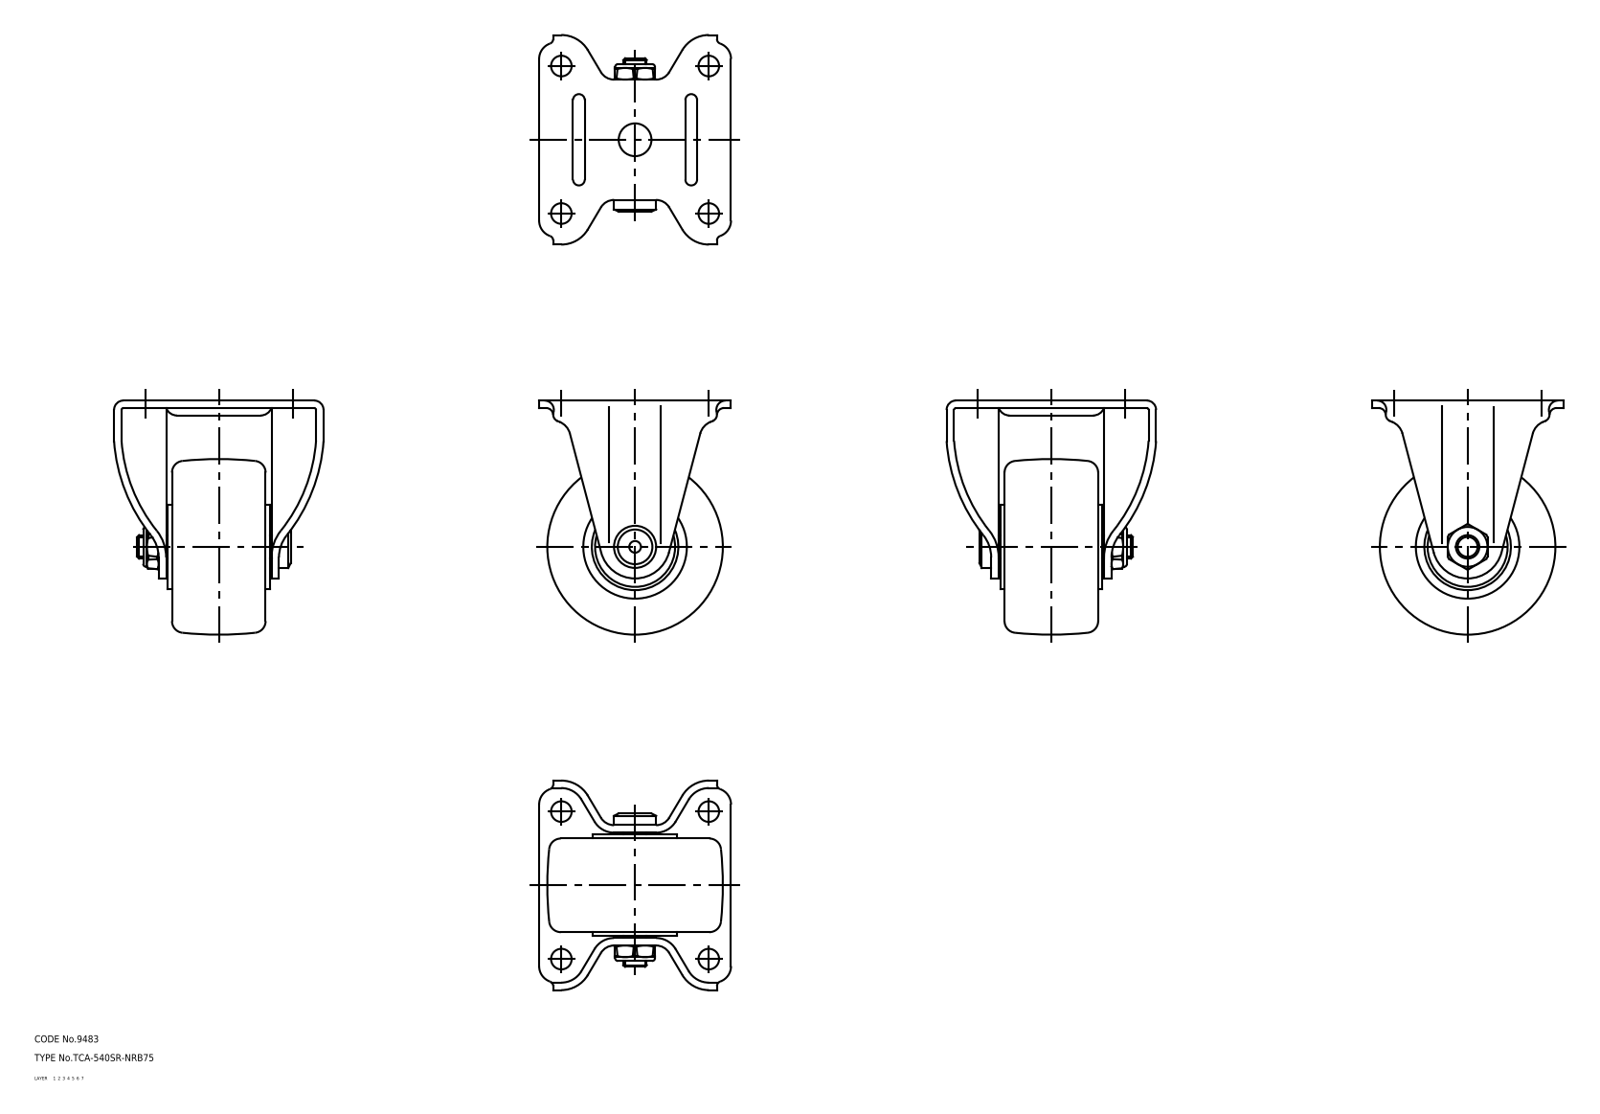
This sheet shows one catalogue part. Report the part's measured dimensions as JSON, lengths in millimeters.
{"part_name": "wheel; axle; No_540SR_NRB75_1298_36", "step_written_by": "CADfix (AUTOMOTIVE_DESIGN)", "units": "millimeters", "bodies": {"solids": 3, "faces": 245, "planar": 0, "cylindrical": 0, "other": 245}, "overall_size": [100, 89.5, 82], "volume_mm3": 217436, "surface_area_mm2": 51578}
